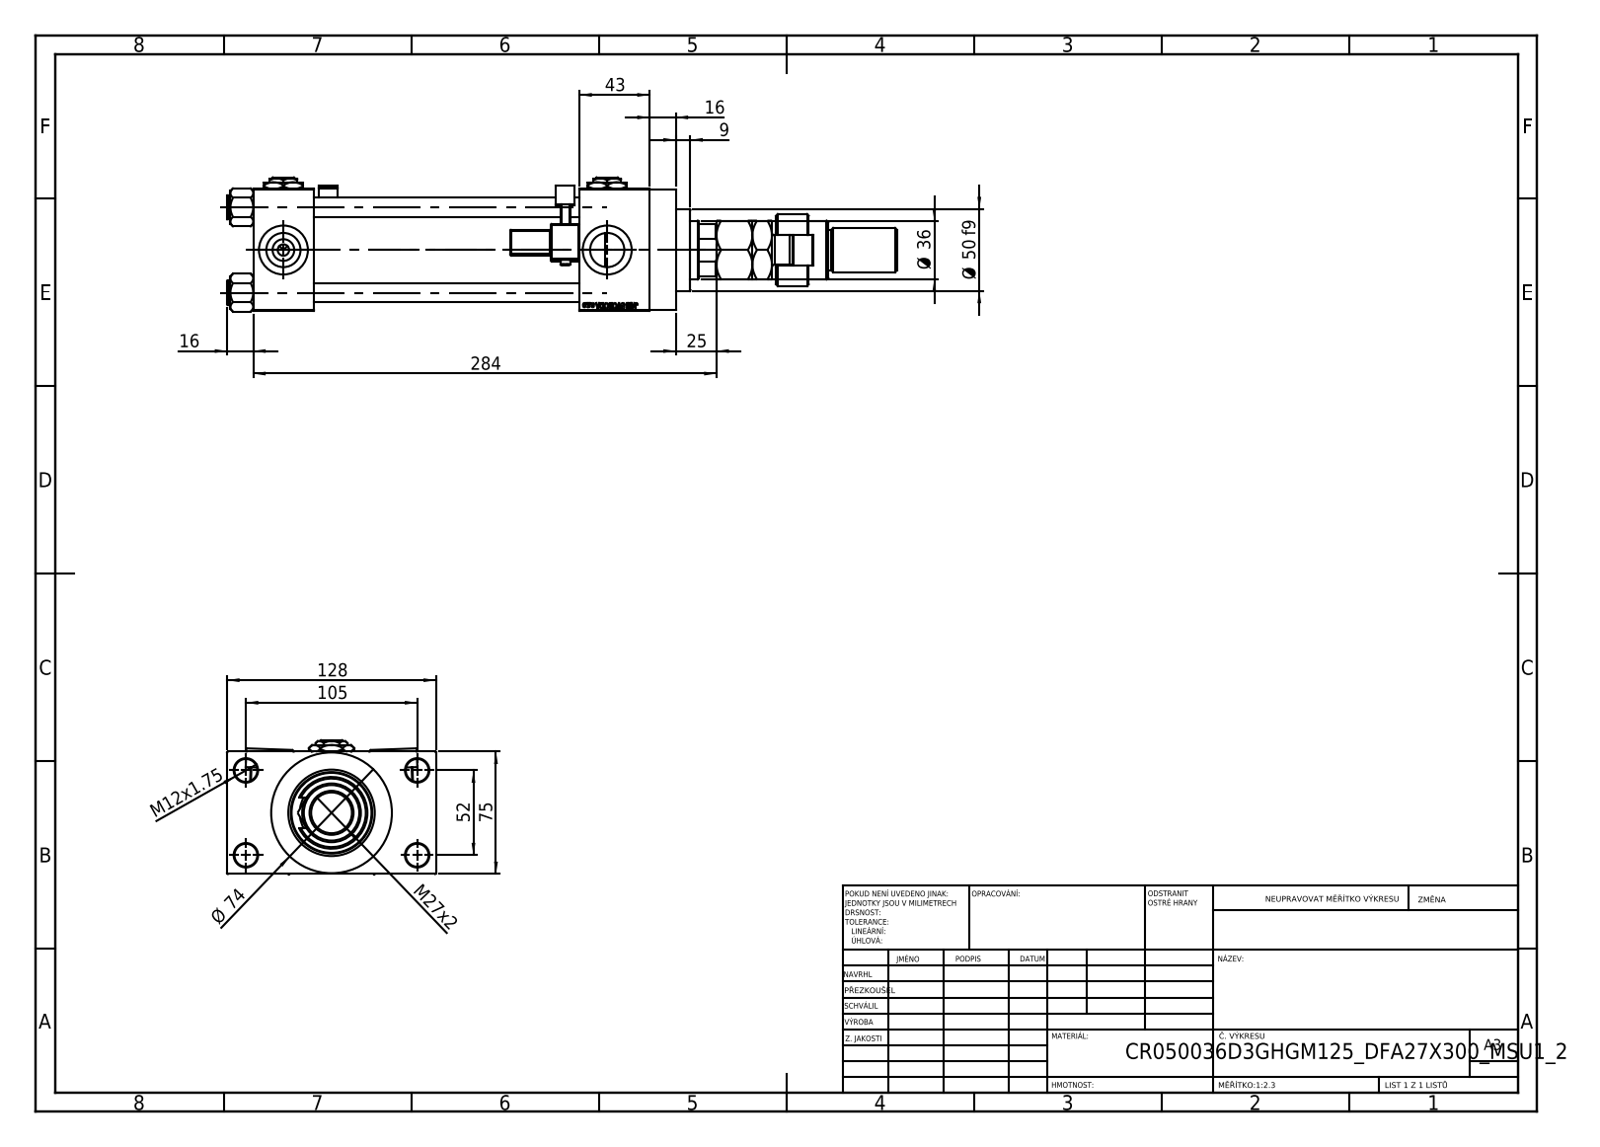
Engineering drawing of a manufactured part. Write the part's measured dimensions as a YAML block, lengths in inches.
part_name: "V215CR_MSU; MFA; V215CR_D_Body; V215CR_D_TYCINKA (+5 more)"
step_written_by: "SolidWorks 2019 (CONFIG_CONTROL_DESIGN)"
units: inches
bodies: {solids: 17, faces: 1443, planar: 631, cylindrical: 172, other: 640}
overall_size: [16.161, 5.039, 3.239]
volume: 70.79
surface_area: 427.5
round_holes:
  - {diameter: 0.472, count: 4}
  - {diameter: 0.551, count: 4}
  - {diameter: 0.825, count: 4}
  - {diameter: 1.181, count: 4}
  - {diameter: 0.276, count: 3}
  - {diameter: 1.004, count: 1}
  - {diameter: 1.535, count: 1}
  - {diameter: 1.614, count: 1}
  - {diameter: 2.087, count: 1}
round_bosses_or_shafts:
  - {diameter: 0.591, count: 4}
  - {diameter: 0.236, count: 2}
  - {diameter: 2.913, count: 1}
  - {diameter: 2.205, count: 1}
  - {diameter: 1.969, count: 1}
  - {diameter: 1.732, count: 1}
  - {diameter: 1.417, count: 1}
  - {diameter: 1.102, count: 1}
partial_cylinders:
  - {radius: 0.02, count: 48}
  - {radius: 0.039, count: 2}
  - {radius: 0.098, count: 2}
  - {radius: 0.157, count: 2}
  - {radius: 0.374, count: 1}
  - {radius: 0.591, count: 1}
  - {radius: 0.689, count: 1}
face_to_face_distances: [2.953, 6.417, 1.457, 7.874, 1.043, 9.567, 1.693, 8.11, 3.996, 2.323]
hole_center_spacings: [1.037, 1.456, 2.059, 2.3, 2.307, 3.096, 3.715, 2.047]
